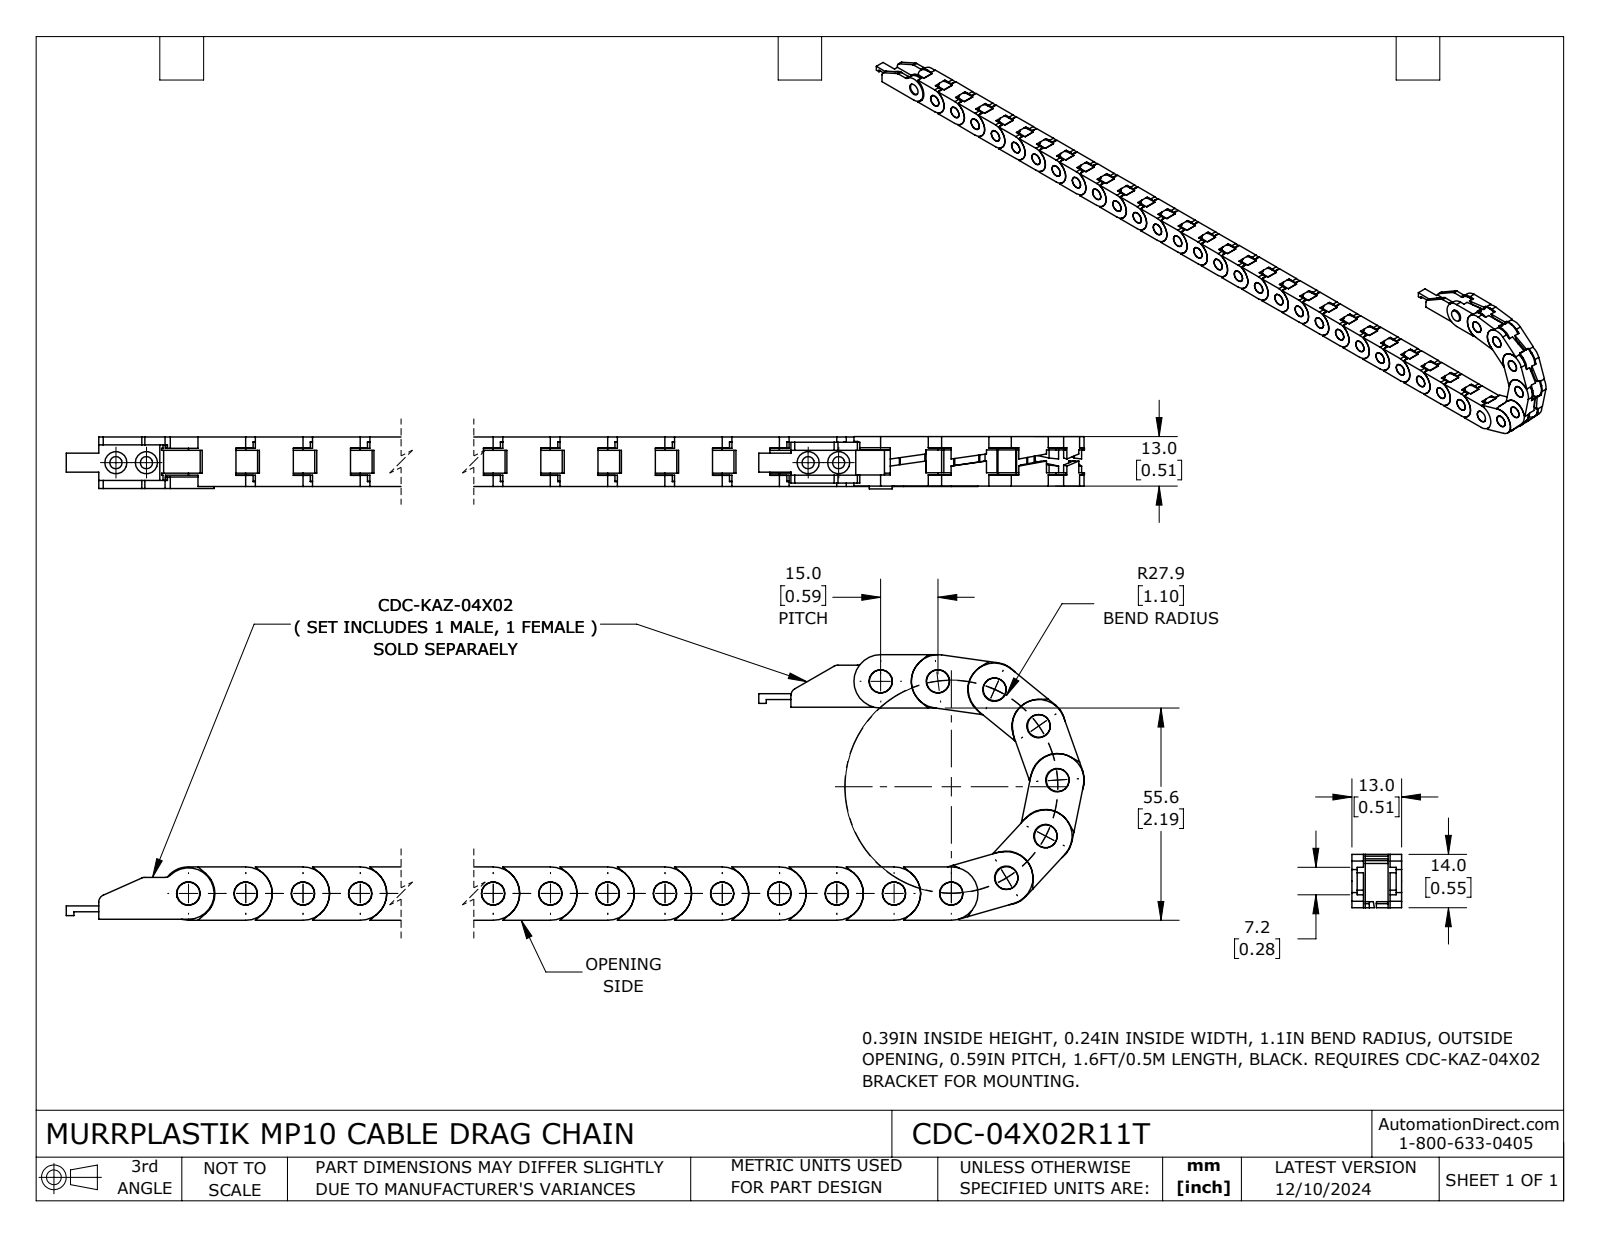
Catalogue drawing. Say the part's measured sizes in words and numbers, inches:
The part is named "CDC-04X02R11T". Its 3-D file was written by "SolidWorks 2024 (AUTOMOTIVE_DESIGN)". It is 37 solids with 2511 faces: 1701 planar, 806 cylindrical and 4 other. Overall it measures 19.169 by 2.738 by 0.539 inches. Its volume is 3.43 cubic inches and its surface area 124.6 square inches. Round holes: 35 of diameter 0.242, 4 of diameter 0.126, 1 of diameter 0.244. Round bosses or shafts: 36 of diameter 0.236, 29 of diameter 0.551. Partial cylindrical surfaces (rounded edges, fillets, slot ends): 175 of radius 0.02, 41 of radius 0.274, 35 of radius 0.142, 35 of radius 0.457, 12 of radius 0.276, 6 of radius 0.079, 2 of radius 0.039, 2 of radius 0.266. The main face-to-face distances are 0.138, 0.374, 0.512, 0.461, 0.051, 0.323, 0.087, 0.134, 0.236, 0.063. The hole center spacings are 0.591, 1.181, 1.772, 2.362, 2.953, 3.543, 4.134, 4.724.
